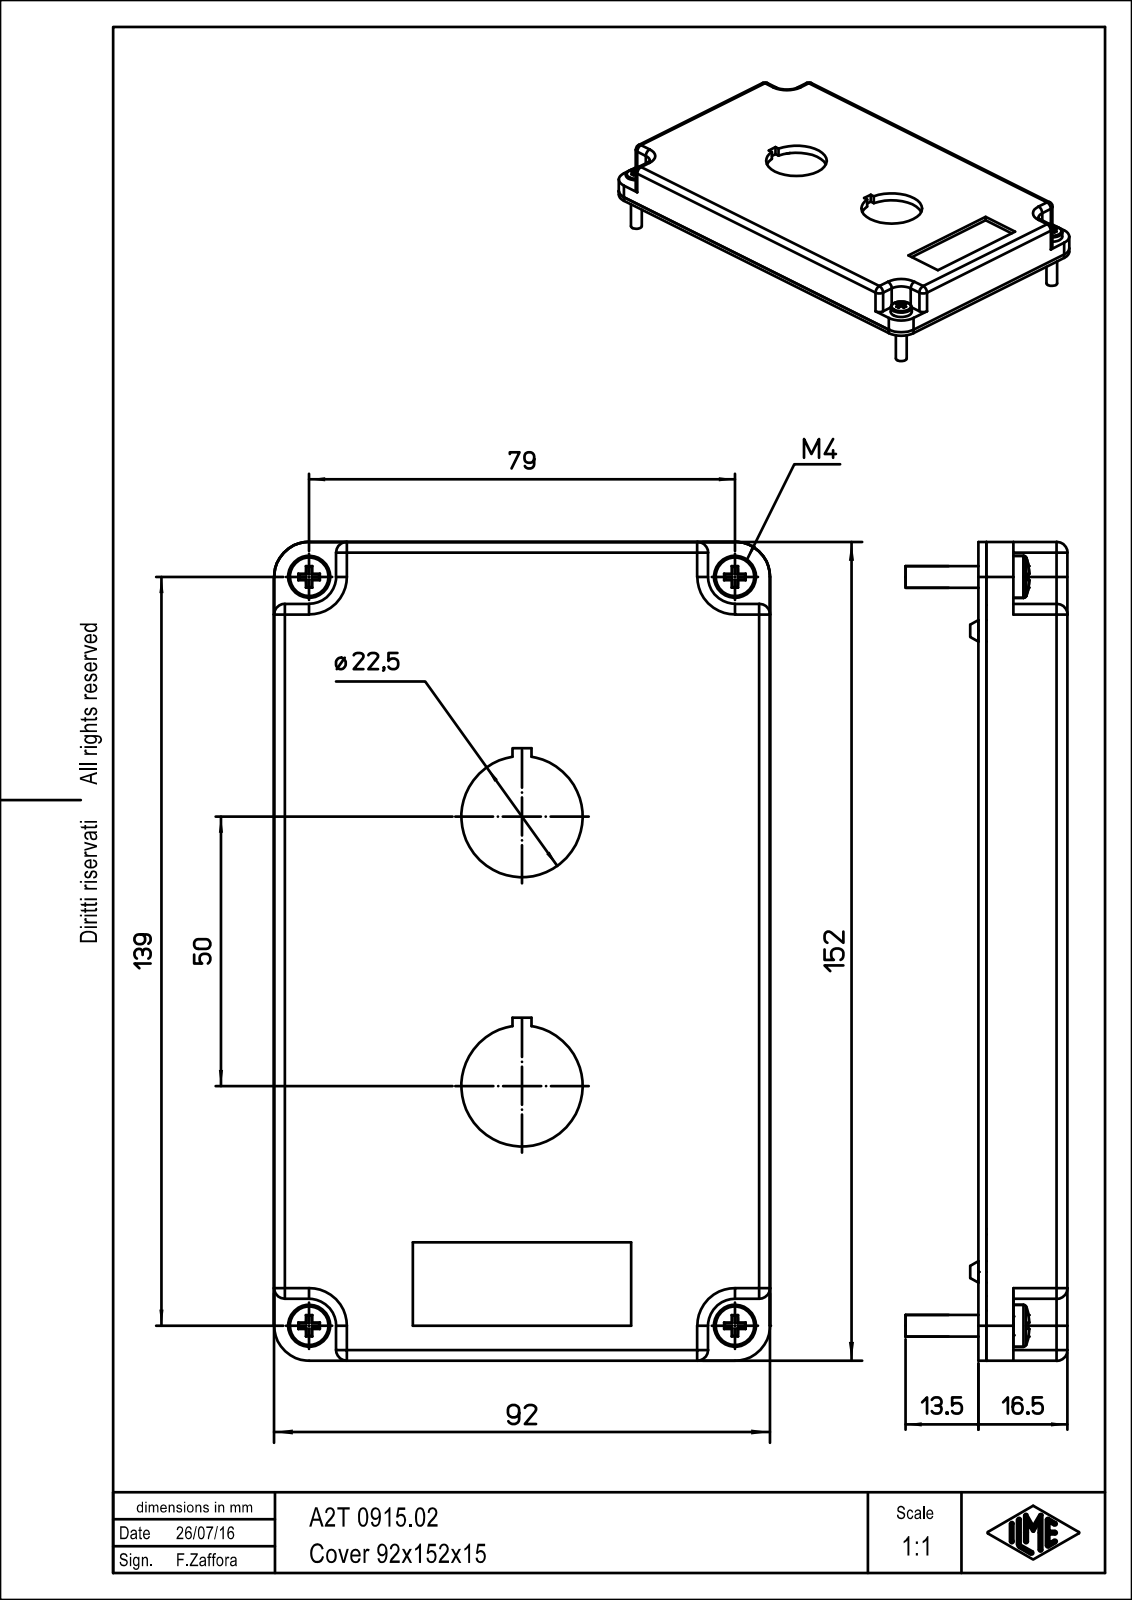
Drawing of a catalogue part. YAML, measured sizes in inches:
part_name: "A2T_0915.02"
step_written_by: "PTC Creo Elements/Direct Modeling 19.0B 21-Mar-2015 (C) Parametric Technology GmbH (AUTOMOTIVE_DESIGN)"
units: inches
bodies: {solids: 1, faces: 574, planar: 432, cylindrical: 106, other: 36}
overall_size: [5.984, 3.623, 1.181]
volume: 4.197
surface_area: 76.33
round_holes:
  - {diameter: 0.177, count: 4}
  - {diameter: 0.886, count: 2}
  - {diameter: 0.13, count: 1}
  - {diameter: 0.228, count: 1}
round_bosses_or_shafts:
  - {diameter: 0.307, count: 4}
  - {diameter: 0.157, count: 4}
  - {diameter: 0.236, count: 2}
  - {diameter: 0.276, count: 1}
  - {diameter: 0.244, count: 1}
partial_cylinders:
  - {radius: 0.079, count: 17}
  - {radius: 0.013, count: 11}
  - {radius: 0.256, count: 8}
  - {radius: 0.197, count: 6}
  - {radius: 0.315, count: 6}
  - {radius: 0.011, count: 2}
  - {radius: 0.011, count: 2}
  - {radius: 0.007, count: 1}
face_to_face_distances: [0.118, 0.531, 0.65, 0.059, 0.591, 0.472, 3.504, 3.622, 5.866, 3.386]
hole_center_spacings: [2.343, 4.032, 3.11, 5.472, 6.294, 0.459, 0.492, 0.729]
